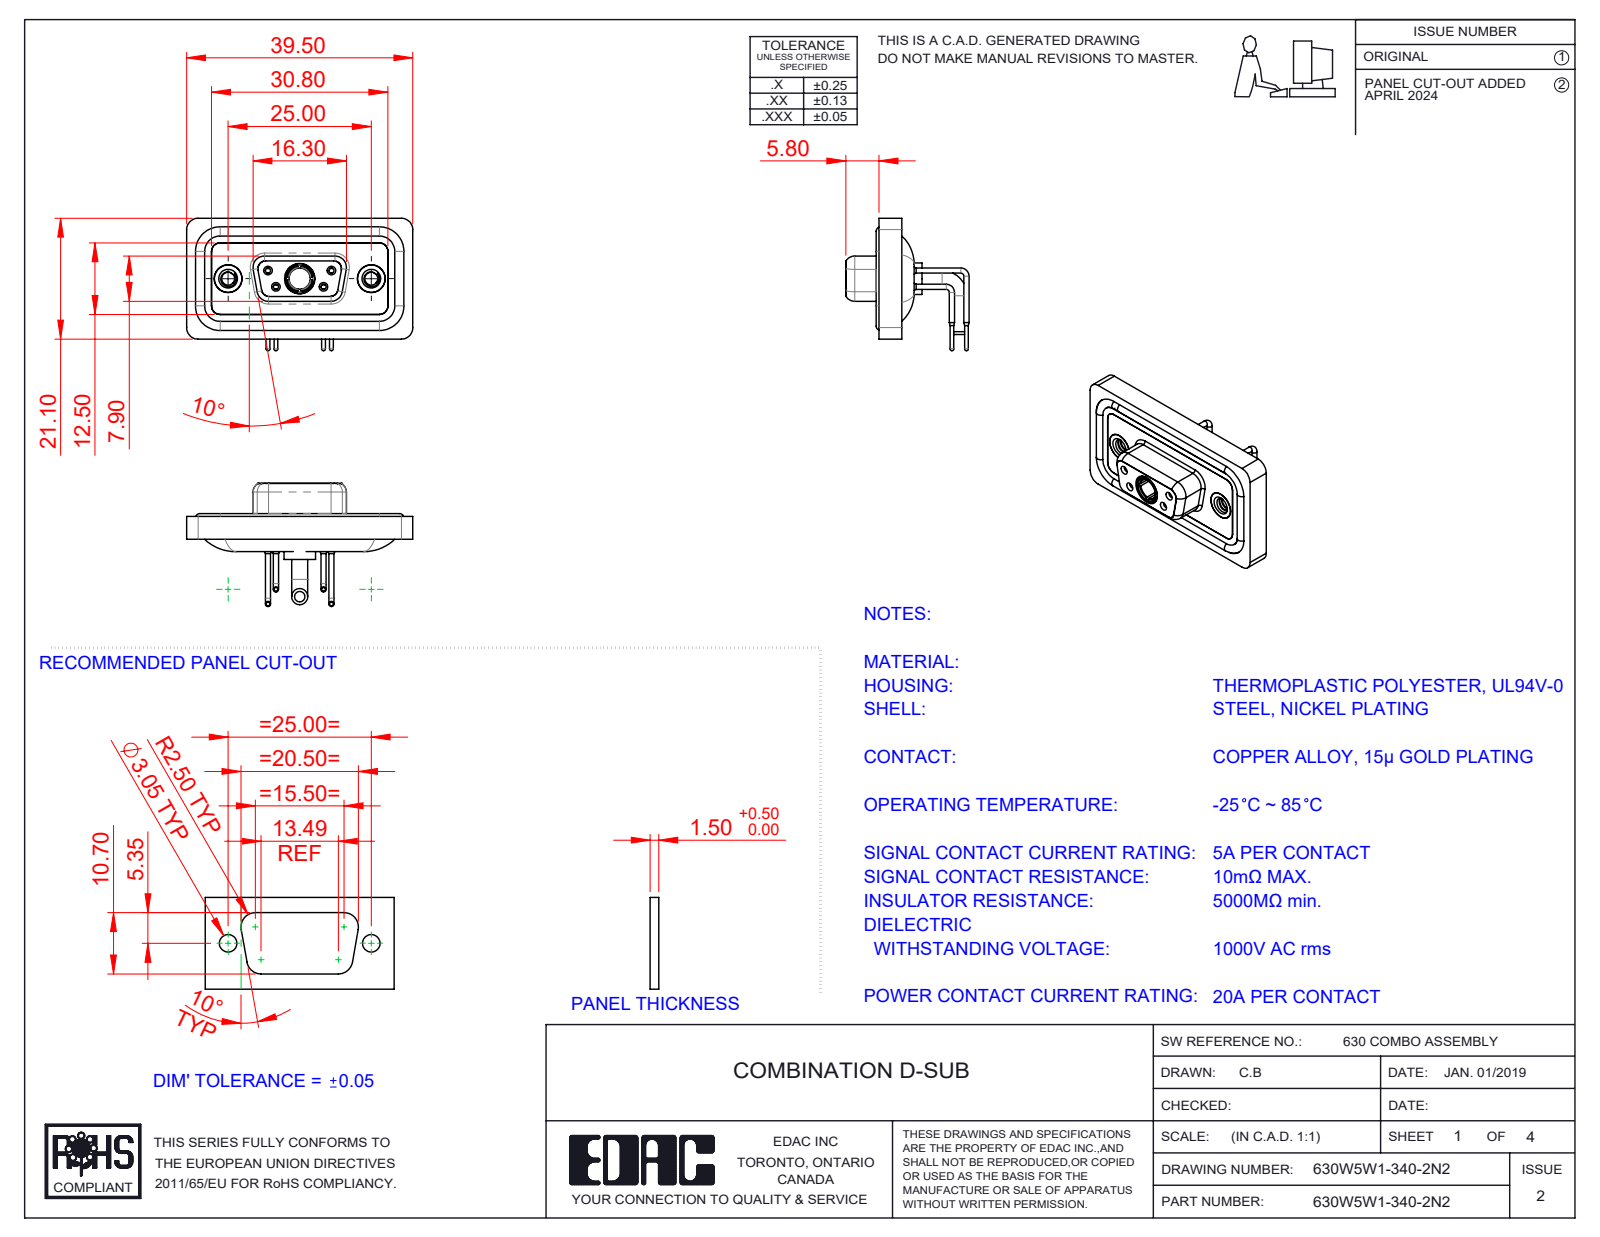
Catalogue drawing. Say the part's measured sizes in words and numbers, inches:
The part is named "630Combo Contact Row 2_50 Contacts; 630Combo Shell Rear_09 Contacts; 630W5W1-340-2N2; 630Combo Waterproof Housing_09 Contacts (+5 more)". Its 3-D file was written by "SolidWorks 2023 (CONFIG_CONTROL_DESIGN)". It is 13 solids with 676 faces: 194 planar, 305 cylindrical and 177 other. Overall it measures 1.555 by 0.91 by 0.848 inches. Its volume is 0.295 cubic inches and its surface area 12.16 square inches. Round holes: 4 of diameter 0.035, 4 of diameter 0.043, 4 of diameter 0.059, 4 of diameter 0.079, 3 of diameter 0.191, 2 of diameter 0.063, 2 of diameter 0.067, 2 of diameter 0.089, 2 of diameter 0.157, 2 of diameter 0.159, 2 of diameter 0.197, 1 of diameter 0.146. Round bosses or shafts: 6 of diameter 0.063, 4 of diameter 0.035, 4 of diameter 0.026, 2 of diameter 0.195, 2 of diameter 0.189, 2 of diameter 0.11, 1 of diameter 0.217, 1 of diameter 0.205. Partial cylindrical surfaces (rounded edges, fillets, slot ends): 18 of radius 0.059, 18 of radius 0.079, 8 of radius 0.053, 8 of radius 0.063, 4 of radius 0.01, 4 of radius 0.02, 4 of radius 0.024, 4 of radius 0.026. The main face-to-face distances are 0.016, 0.071, 0.043, 0.114, 0.098, 0.063, 0.122, 0.083, 0.059, 0.02. The hole center spacings are 0.124, 0.225, 0.28, 0.492, 0.713, 0.173, 0.173, 0.327.
